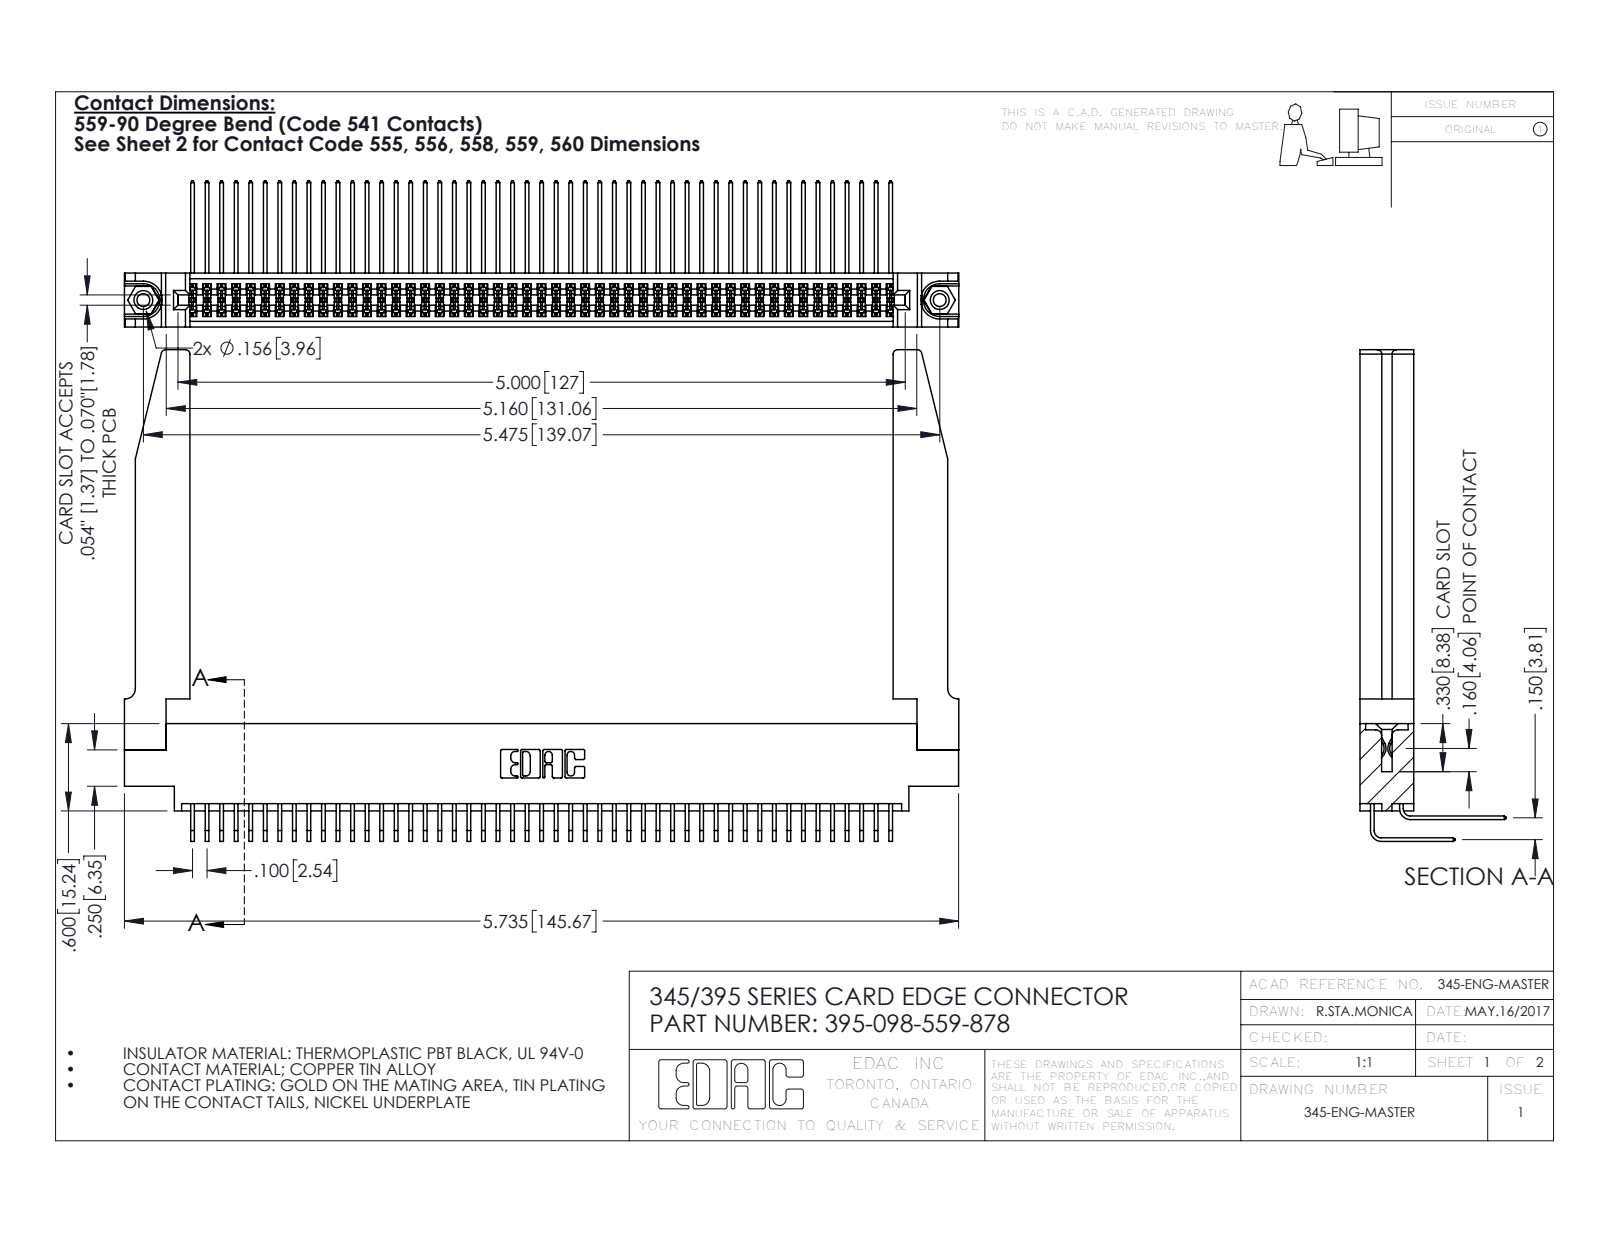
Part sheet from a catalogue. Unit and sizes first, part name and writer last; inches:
Units: inches
Overall size (bounding box): 5.736 × 3.379 × 1.005
Round holes (diameter × count): ⌀0.089 ×2, ⌀0.125 ×2, ⌀0.156 ×2, ⌀0.064 ×1
Round bosses / shafts (diameter × count): ⌀0.155 ×2
Partial cylindrical surfaces — rounded edges, fillets, slot ends (radius × count): R0.006 ×147, R0.01 ×22, R0.03 ×8, R0.007 ×6, R0.031 ×6, R0.026 ×3, R0.014 ×2, R0.019 ×2
Main face-to-face distances: 0.072, 0.37, 0.298, 0.098, 0.272, 0.025, 0.2, 0.225, 0.15, 0.175
Hole centre spacings: 0.27, 5.239, 5.475
Volume: 1.369 in³ · Surface area: 48.76 in²
Bodies: 103 solids, 5460 faces (3656 planar, 1752 cylindrical, 52 other)
Part name (STEP PRODUCT): 345 Part_0.170 Offset - 0.156 Dia-TH; 345-292-001_558 559 Tail - 1; 345-220-078_345-220-078; 345-250-001_345-250-001-102 (+2 more)
STEP written by: SolidWorks 2016 (CONFIG_CONTROL_DESIGN)
